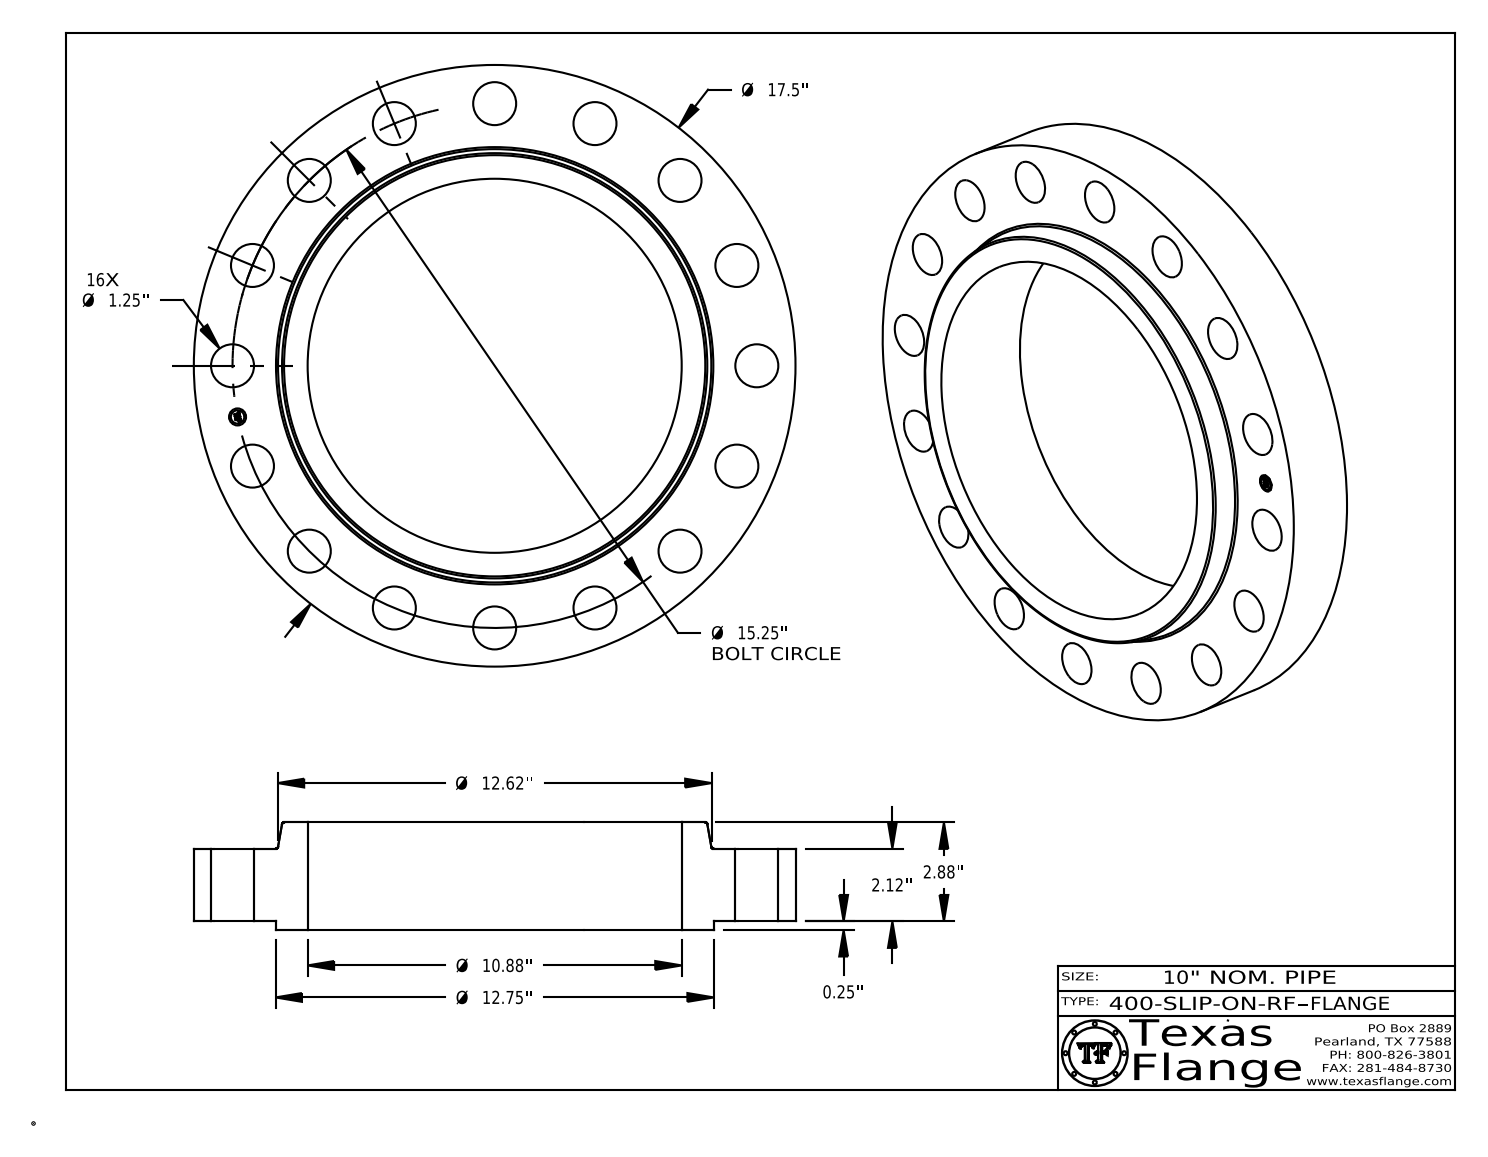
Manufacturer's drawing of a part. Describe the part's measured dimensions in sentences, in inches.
The part is named "400-SLIP-ON-RF". Its 3-D file was written by "CATIA V5 STEP AP214 (AUTOMOTIVE_DESIGN)". It is 1 solid with 433 faces: 369 planar, 58 cylindrical and 6 other. Overall it measures 17.5 by 17.5 by 3.13 inches. Its volume is 302.3 cubic inches and its surface area 646.4 square inches. Round holes: 16 of diameter 1.25, 1 of diameter 0.495, 1 of diameter 10.88. Round bosses or shafts: 8 of diameter 0.03, 1 of diameter 17.5, 1 of diameter 12.75, 1 of diameter 0.39. The main face-to-face distances are 2.12, 0.25, 2.37, 3.13, 2.88, 0.76, 0.015, 2.355, 2.105, 0.775. The hole center spacings are 8.472, 10.783, 14.957, 14.089, 7.625, 2.975, 2.975, 5.836.
